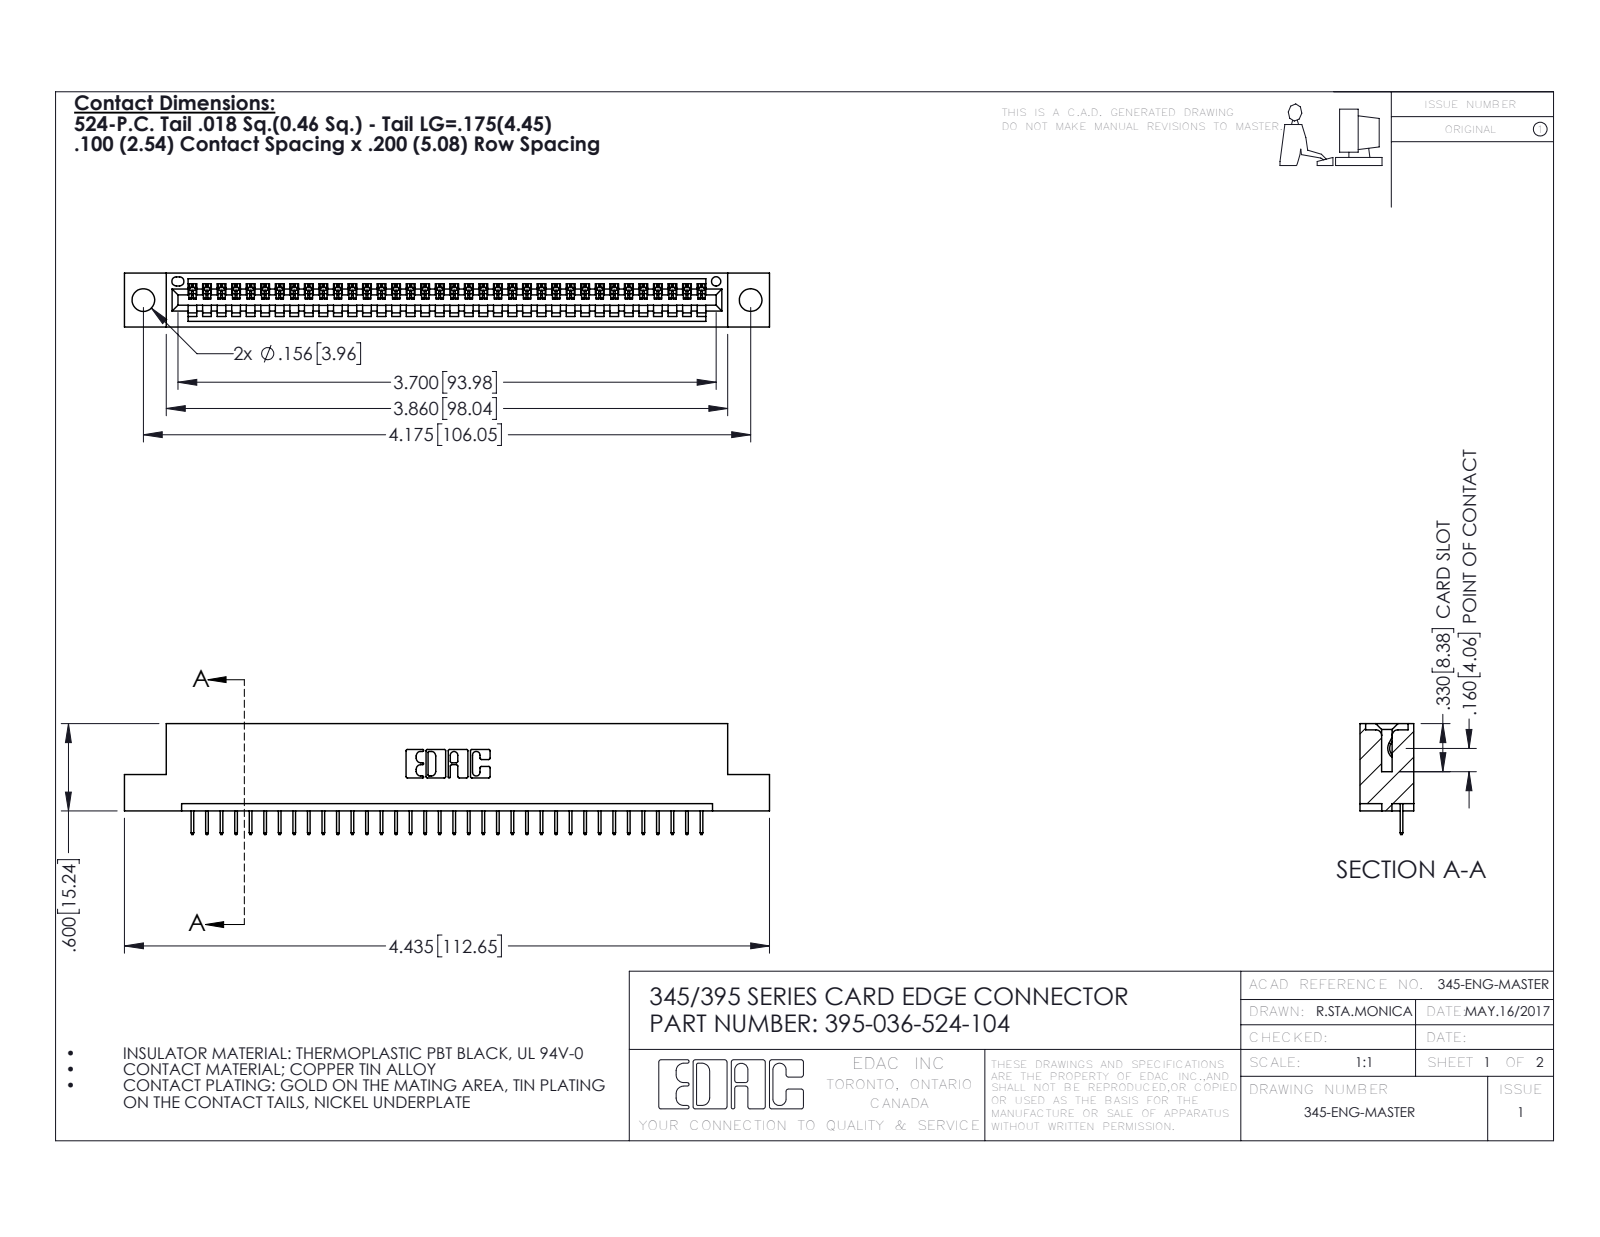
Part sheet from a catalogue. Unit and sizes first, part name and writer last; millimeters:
Units: millimetres
Overall size (bounding box): 112.6 × 19.4 × 9.4
Round holes (diameter × count): ⌀4 ×2, ⌀1.6 ×1
Partial cylindrical surfaces — rounded edges, fillets, slot ends (radius × count): R0.2 ×72, R0.3 ×22, R0.2 ×6, R0.8 ×6, R0.7 ×3, R0.8 ×2, R1 ×2, R0.4 ×1
Main face-to-face distances: 7.6, 1.8, 9.4, 5.1, 2.5, 6.9, 0.6, 5.7, 1.8, 3.8
Hole centre spacings: 6.9, 100.1, 106
Volume: 10 400 mm³ · Surface area: 13 120 mm²
Bodies: 37 solids, 2358 faces (1736 planar, 622 cylindrical, 0 other)
Part name (STEP PRODUCT): 345 Part_Flush Mounting Lugs - 0.156 Dia-TH; 395-036-524-104; 345-292-001_345-293-124
STEP written by: SolidWorks 2016 (CONFIG_CONTROL_DESIGN)
